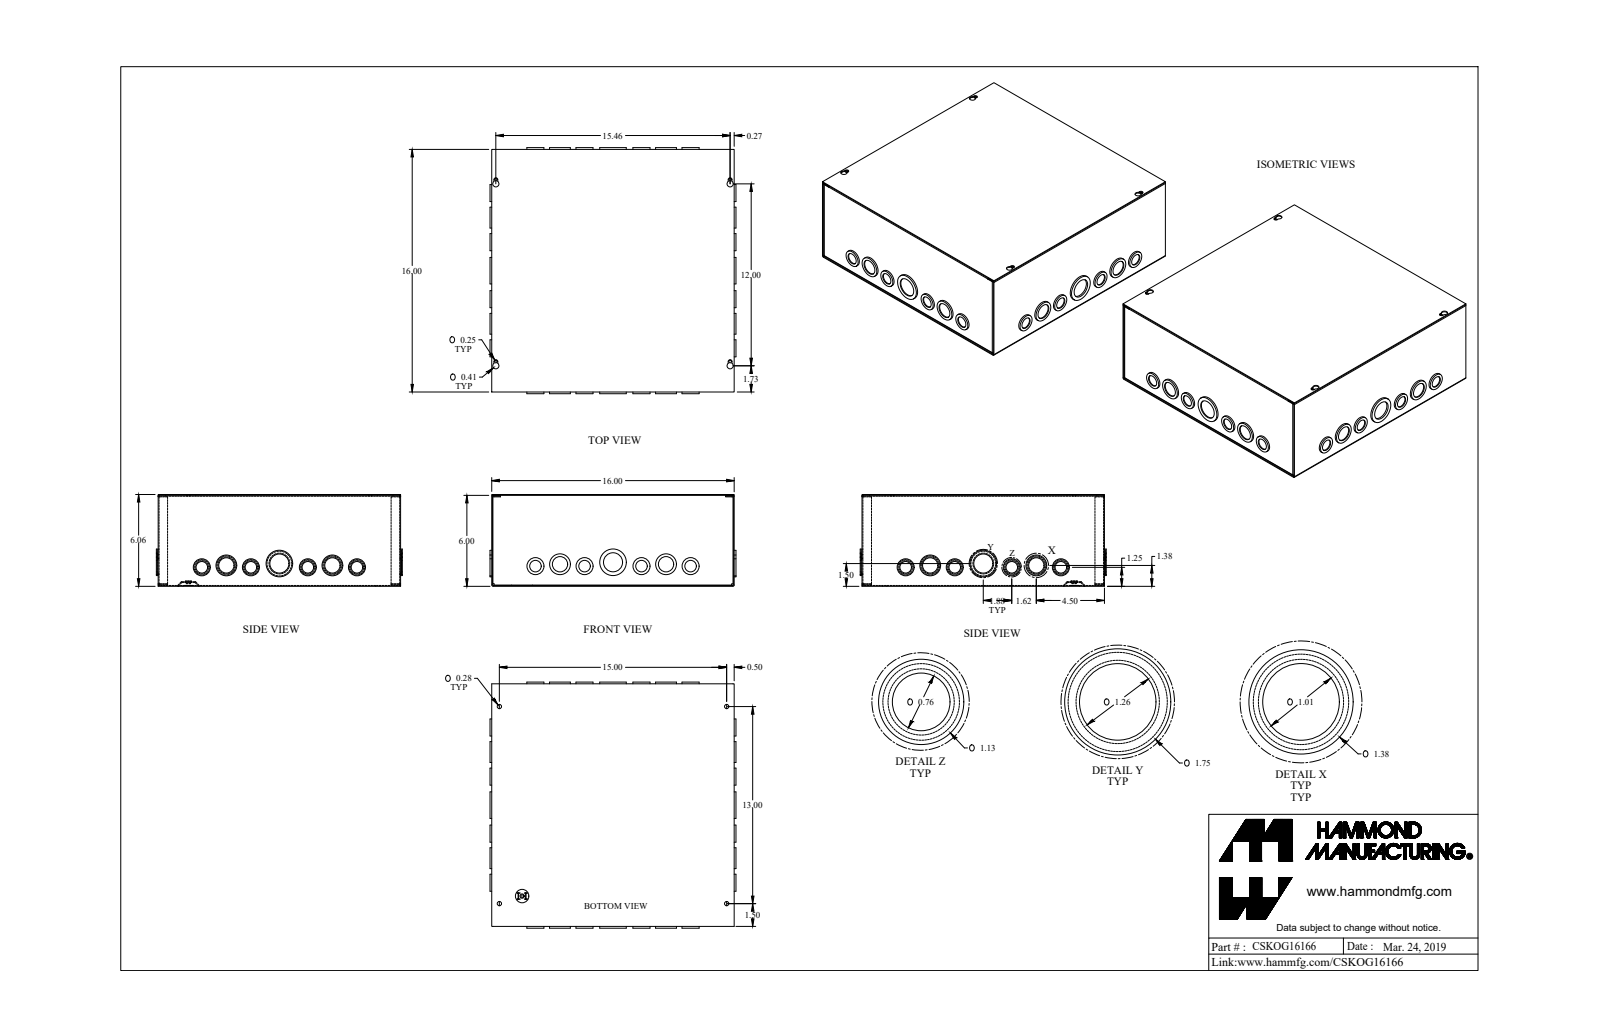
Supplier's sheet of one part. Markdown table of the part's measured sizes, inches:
| quantity | value |
| --- | --- |
| part name | CSKOG16166 |
| STEP written by | SolidWorks 2019 (AUTOMOTIVE_DESIGN) |
| units | inches |
| bodies | 5 solids, 423 faces (250 planar, 166 cylindrical, 7 other) |
| overall size | 16.234 × 16.234 × 6.057 |
| volume | 54.27 in³ |
| surface area | 1 938 in² |
| round holes (diameter × count) | 1.011 × 12, 0.761 × 8, 1.261 × 6, 0.17 × 5, 0.281 × 4, 1.636 × 2, 0.5 × 1 |
| round bosses / shafts (diameter × count) | 1.125 × 10, 0.875 × 8, 1.375 × 5, 1.125 × 4, 0.875 × 4, 1.75 × 2, 1.375 × 1, 0.492 × 1 |
| partial cylindrical surfaces (radius × count) | 0.029 × 12, 0.086 × 12, 0.057 × 8, 0.125 × 4, 0.203 × 4 |
| main face-to-face distances | 0.057, 6, 15.943, 5.943, 6.057, 16, 15.886, 0.114, 0.08, 5.863 |
| hole center spacings | 1.625, 7, 0.55, 1.896, 3.24, 3.502, 5.126, 5.381 |
